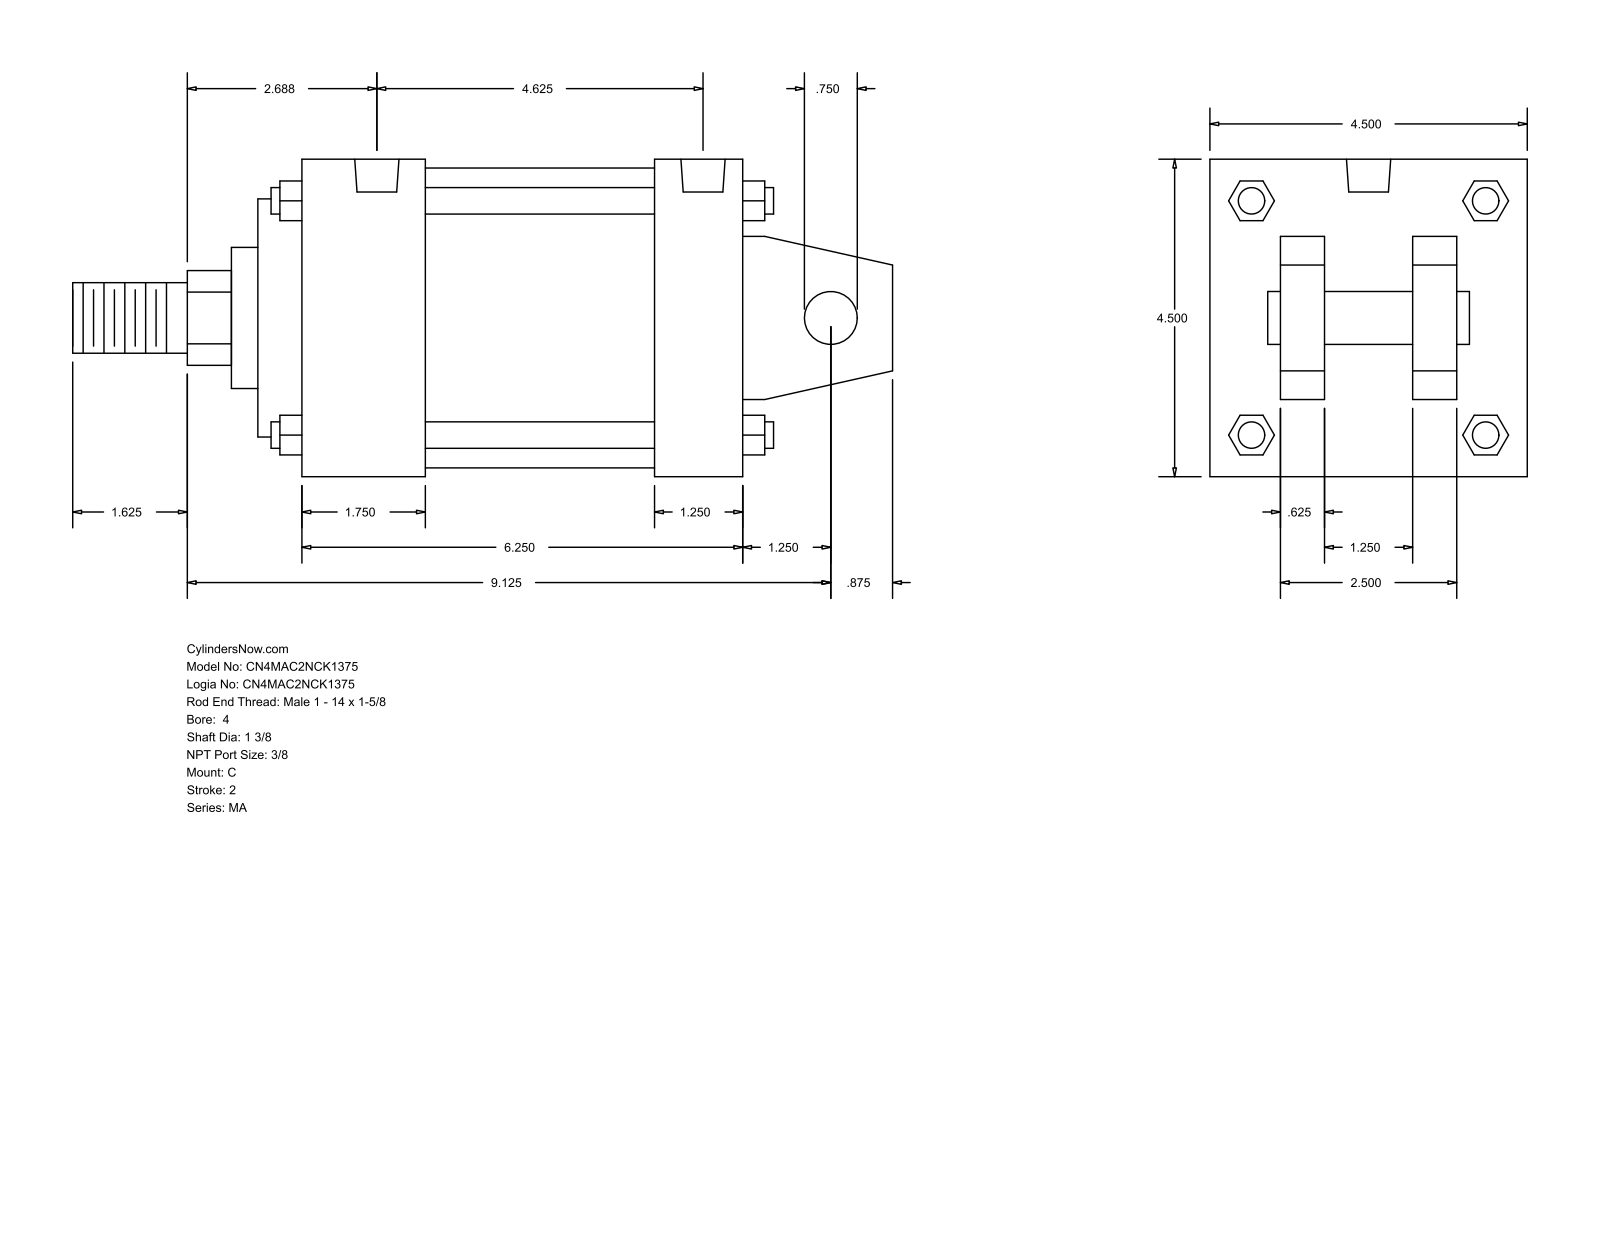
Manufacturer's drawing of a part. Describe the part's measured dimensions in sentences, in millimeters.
The part is named "MA_C__0400_1.375". Its 3-D file was written by "GSSL Pune (CONFIG_CONTROL_DESIGN)". It is 0 solids with 141 faces: 109 planar, 32 cylindrical and 0 other. Overall it measures 295.27 by 114.3 by 114.3 millimeters. Round holes: 4 of diameter 11.11, 2 of diameter 15.93. Round bosses or shafts: 4 of diameter 9.53, 1 of diameter 107.95, 1 of diameter 85.72, 1 of diameter 50.8, 1 of diameter 34.92, 1 of diameter 25.4, 1 of diameter 19.05. Partial cylindrical surfaces (rounded edges, fillets, slot ends): 1 of radius 17.06. The main face-to-face distances are 114.3, 15.87, 158.76, 73.03, 41.27, 25.4, 88.9, 47.63, 174.63, 142.88. The hole center spacings are 4.77, 107.94, 112.71, 117.48.
